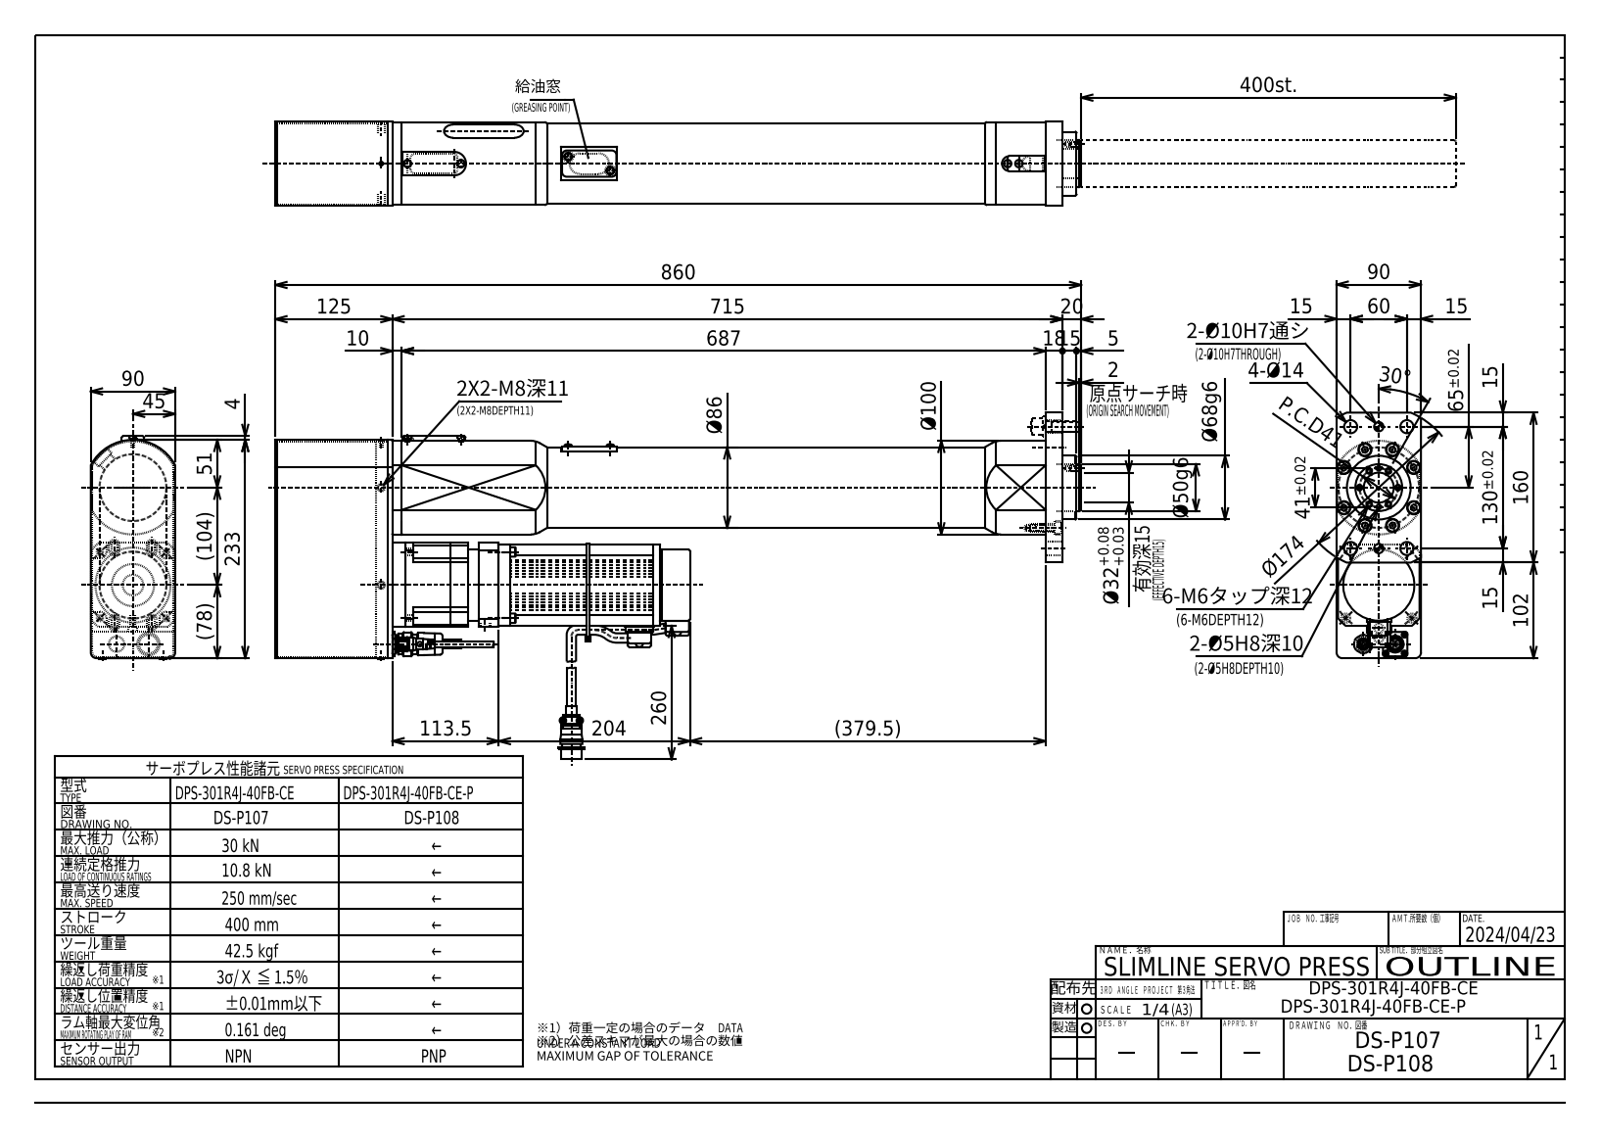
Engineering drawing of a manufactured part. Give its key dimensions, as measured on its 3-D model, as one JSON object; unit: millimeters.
{"part_name": "DPS-301R4J-40FB-CE-X(17P-21023)_20230714", "step_written_by": "Autodesk Inventor 2023 (CONFIG_CONTROL_DESIGN)", "units": "millimeters", "bodies": {"solids": 1, "faces": 1806, "planar": 1019, "cylindrical": 513, "other": 274}, "overall_size": [860, 263.5, 90], "volume_mm3": 9292000, "surface_area_mm2": 569368, "round_holes": [[6.65, 12], [14, 12], [4.92, 10], [5.5, 10], [9, 8], [4.2, 6], [9.5, 6], [8, 4], [5, 3], [4.5, 2], [10, 2], [11, 2]], "round_bosses_or_shafts": [[8, 16], [13, 8], [7, 6], [3, 6], [10, 4], [8.5, 4], [7.5, 4], [4, 4]], "partial_cylinders_radius": [[0.6, 48], [1, 26], [0.3, 20], [2, 16], [3, 10], [4.5, 10], [5, 10], [1.5, 8]], "face_to_face_distances": [1.5, 90, 1, 3, 88.5, 89, 4.5, 16.5, 7.5, 6], "hole_center_spacings": [20.5, 43, 27.25, 61.61, 80.82, 10.61, 23.09, 24.75]}
